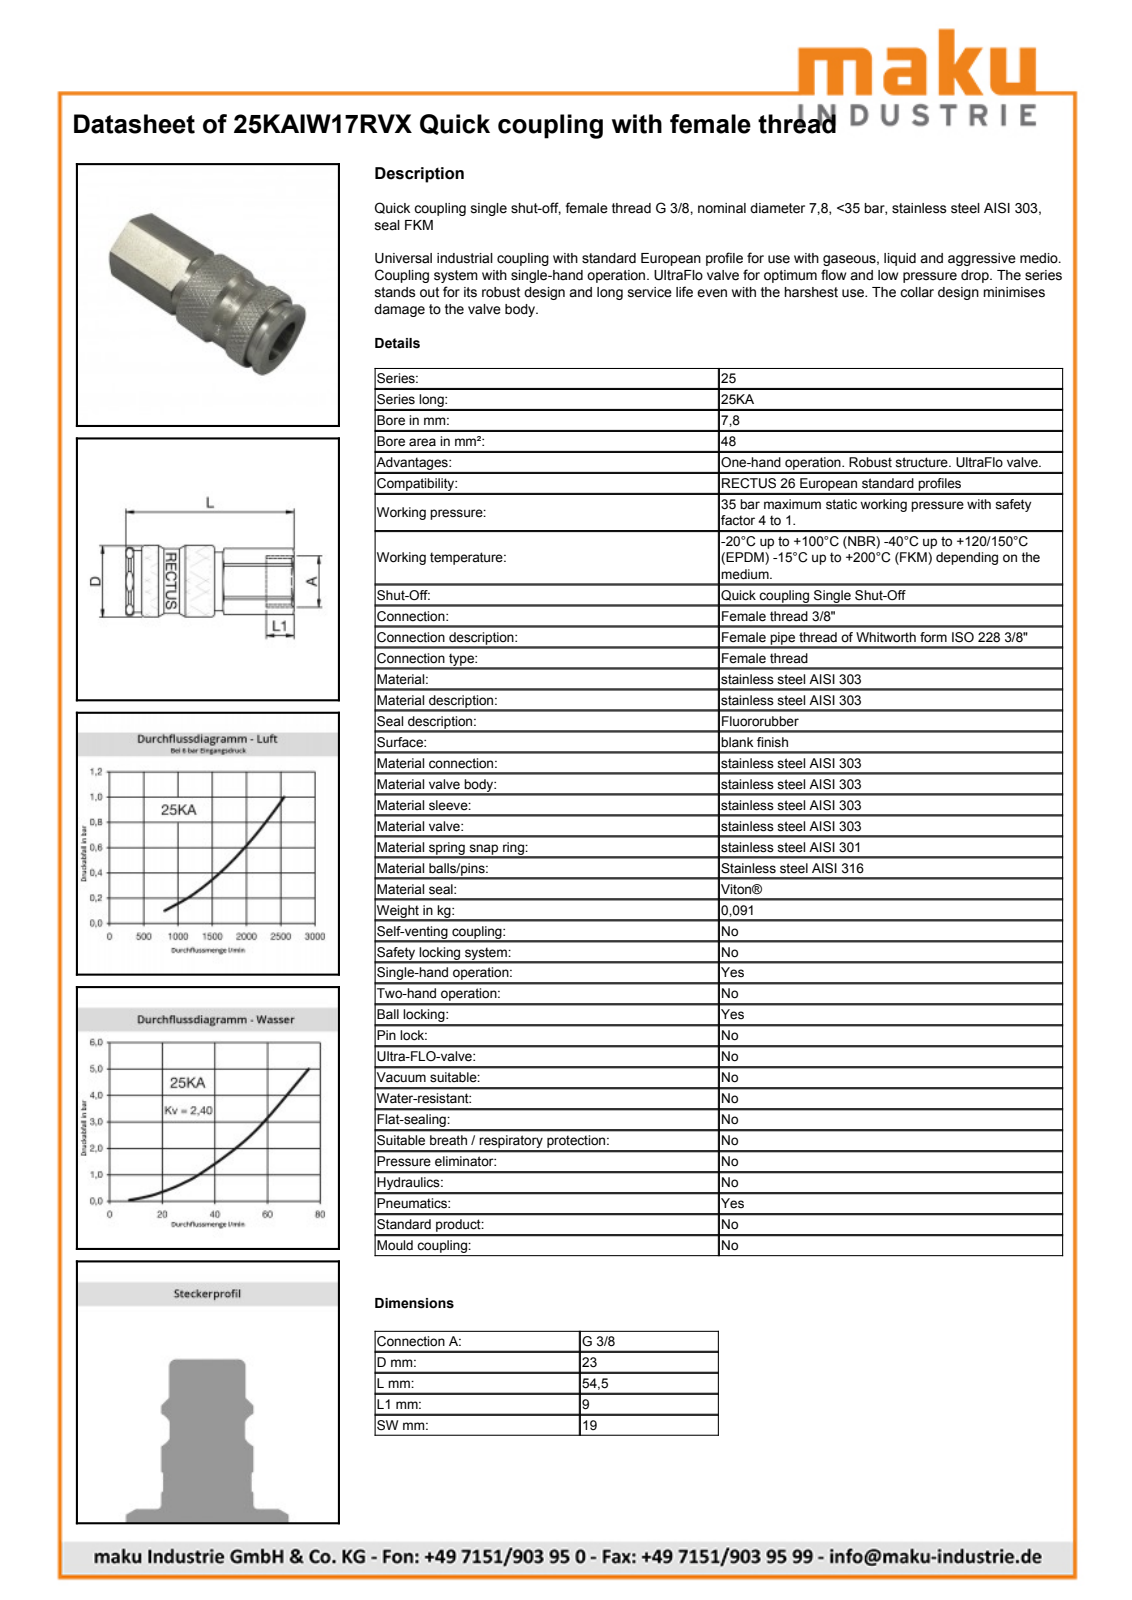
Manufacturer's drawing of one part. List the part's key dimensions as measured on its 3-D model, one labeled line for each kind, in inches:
Part name (STEP PRODUCT): D112793
STEP written by: Autodesk Inventor 2013 (AUTOMOTIVE_DESIGN)
Units: inches
Bodies: 2 solids, 613 faces (211 planar, 85 cylindrical, 317 other)
Overall size (bounding box): 2.264 × 0.911 × 0.911
Volume: 1.041 in³ · Surface area: 12.91 in²
Round holes (diameter × count): ⌀0.394 ×1, ⌀0.589 ×1, ⌀0.63 ×1, ⌀0.679 ×1, ⌀0.762 ×1, ⌀0.789 ×1
Round bosses / shafts (diameter × count): ⌀0.911 ×1, ⌀0.827 ×1, ⌀0.787 ×1, ⌀0.746 ×1, ⌀0.602 ×1, ⌀0.597 ×1
Partial cylindrical surfaces — rounded edges, fillets, slot ends (radius × count): R0.409 ×1, R0.421 ×1, R0.433 ×1
Main face-to-face distances: 0.748, 1.909, 1.132, 0.965, 0.945, 0.207, 0.758, 0.354, 1.299, 2.264
